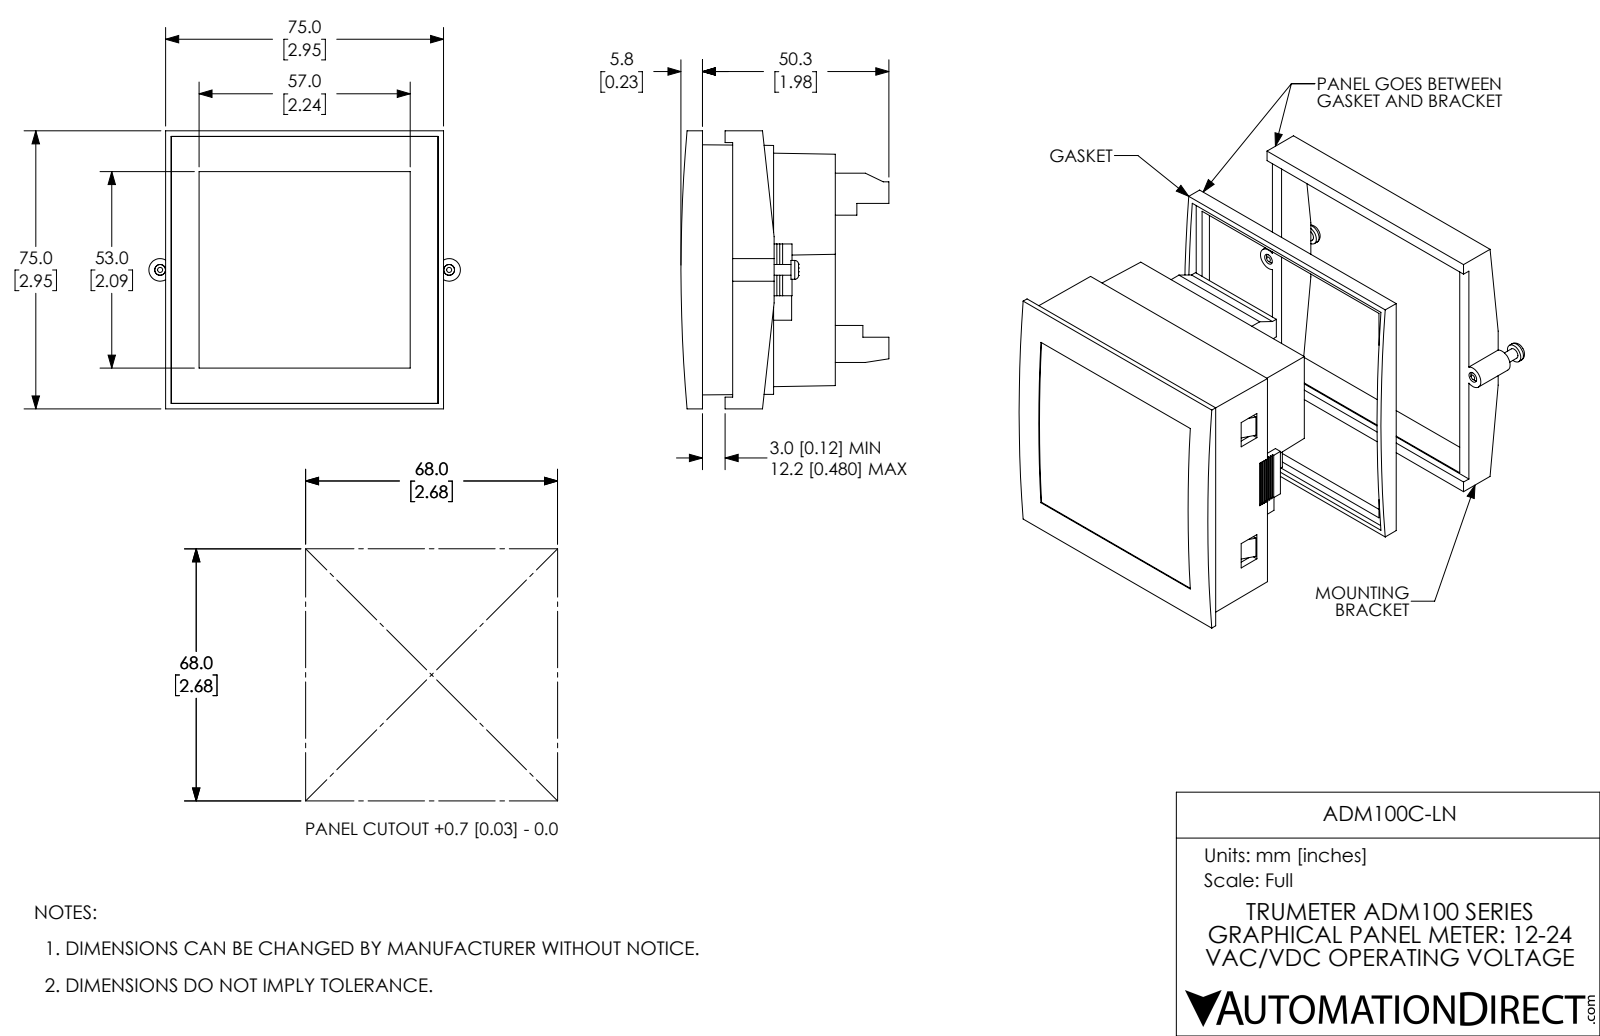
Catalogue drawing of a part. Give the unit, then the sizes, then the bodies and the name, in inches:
Units: inches
Overall size (bounding box): 3.311 × 2.953 × 2.209
Round holes (diameter × count): ⌀0.151 ×13, ⌀0.115 ×2
Round bosses / shafts (diameter × count): ⌀0.148 ×13, ⌀0.2 ×2, ⌀0.114 ×2
Partial cylindrical surfaces — rounded edges, fillets, slot ends (radius × count): R0.12 ×2, R17.037 ×2
Main face-to-face distances: 0.075, 0.305, 0.236, 2.717, 2.657, 0.089, 0.148, 2.805, 2.583, 1.142
Hole centre spacings: 1.653, 0.2, 1.677, 0.4, 1.724, 0.6, 1.792, 0.8
Volume: 9.565 in³ · Surface area: 90.64 in²
Bodies: 23 solids, 419 faces (335 planar, 76 cylindrical, 8 other)
Part name (STEP PRODUCT): ADM100C-LN
STEP written by: SolidWorks 2021 (CONFIG_CONTROL_DESIGN)
